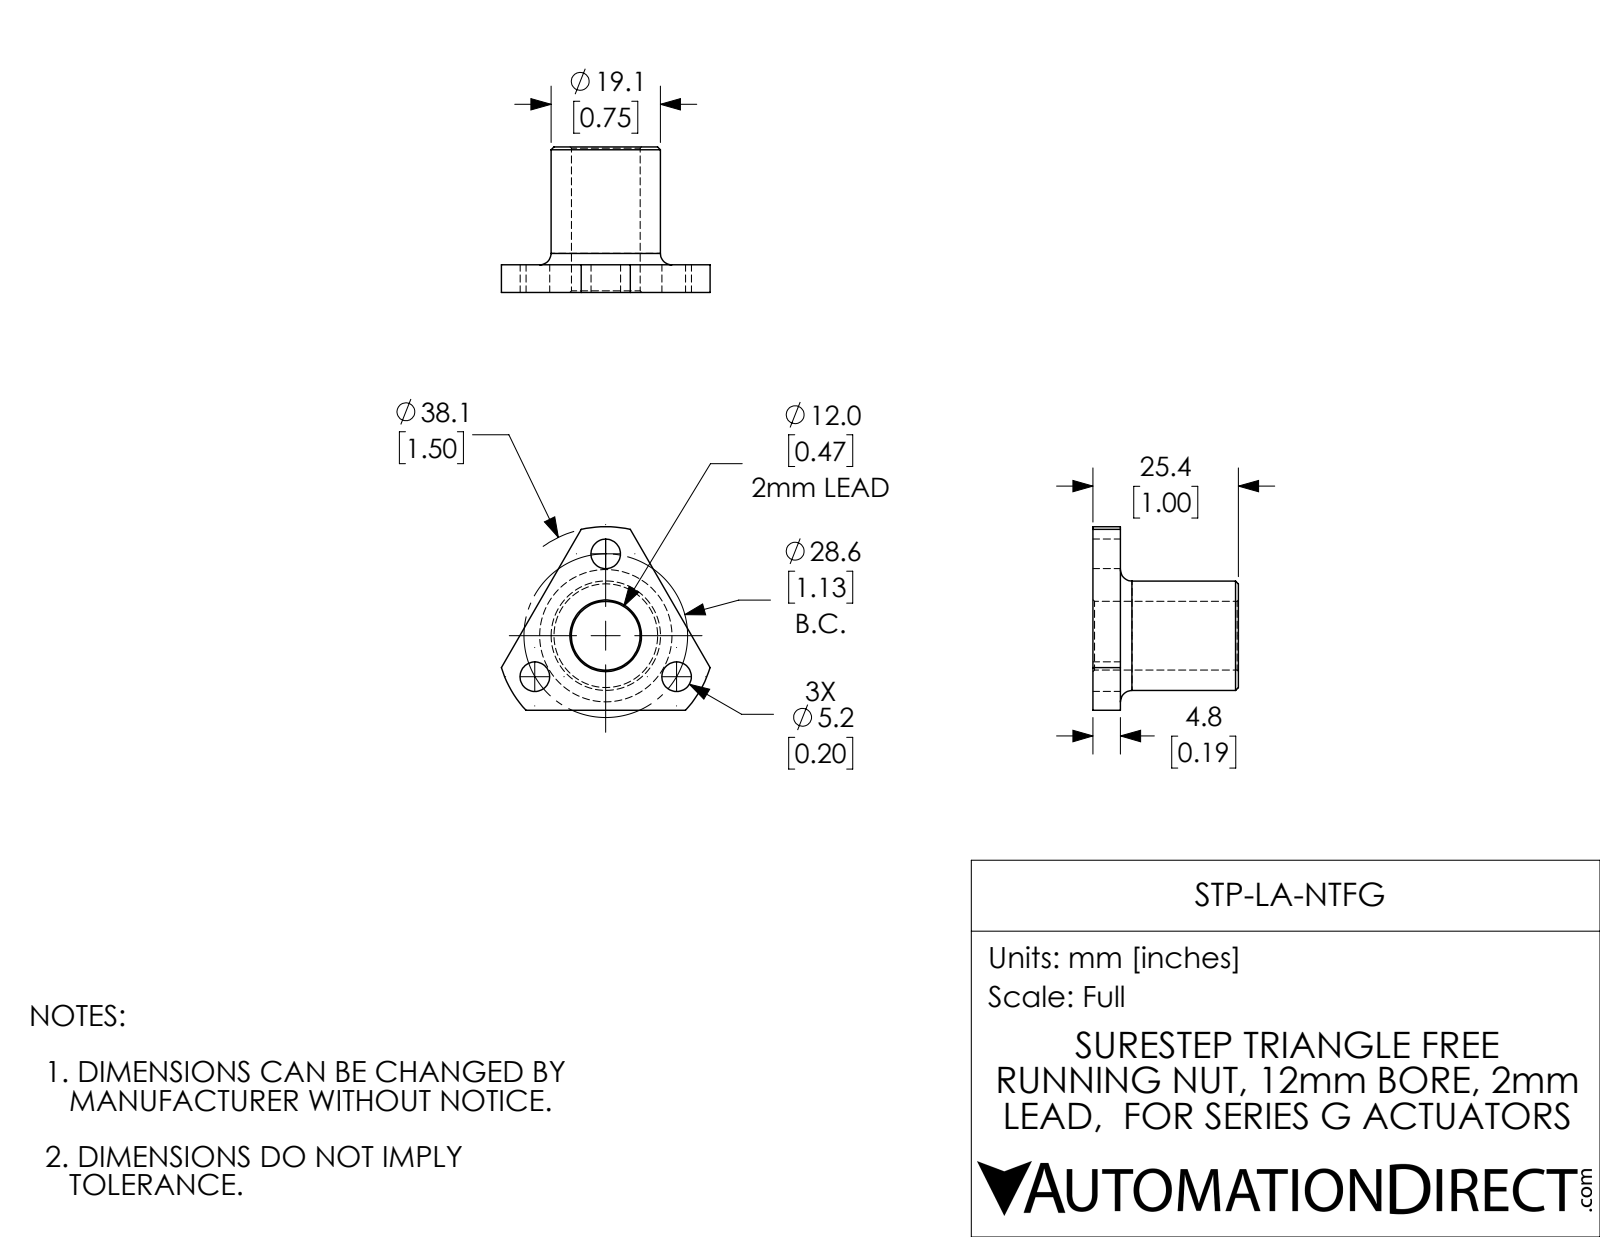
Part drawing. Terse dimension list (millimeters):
name: STP-LA-NTFG
written by: SolidWorks 2017 (AUTOMOTIVE_DESIGN)
unit: mm
bodies: 1 solid, 27 faces (6 planar, 13 cylindrical, 8 other)
size: 36.44 × 32.05 × 25.4
volume: 6 570 mm³; area: 4 103 mm²
holes: 3× ⌀5.16, 1× ⌀12
bosses: 1× ⌀19.1
rounds: 1× R19.05
face distances: 4.8, 20.6, 25.4
hole spacings: 14.29, 24.76, 14.3, 24.75
